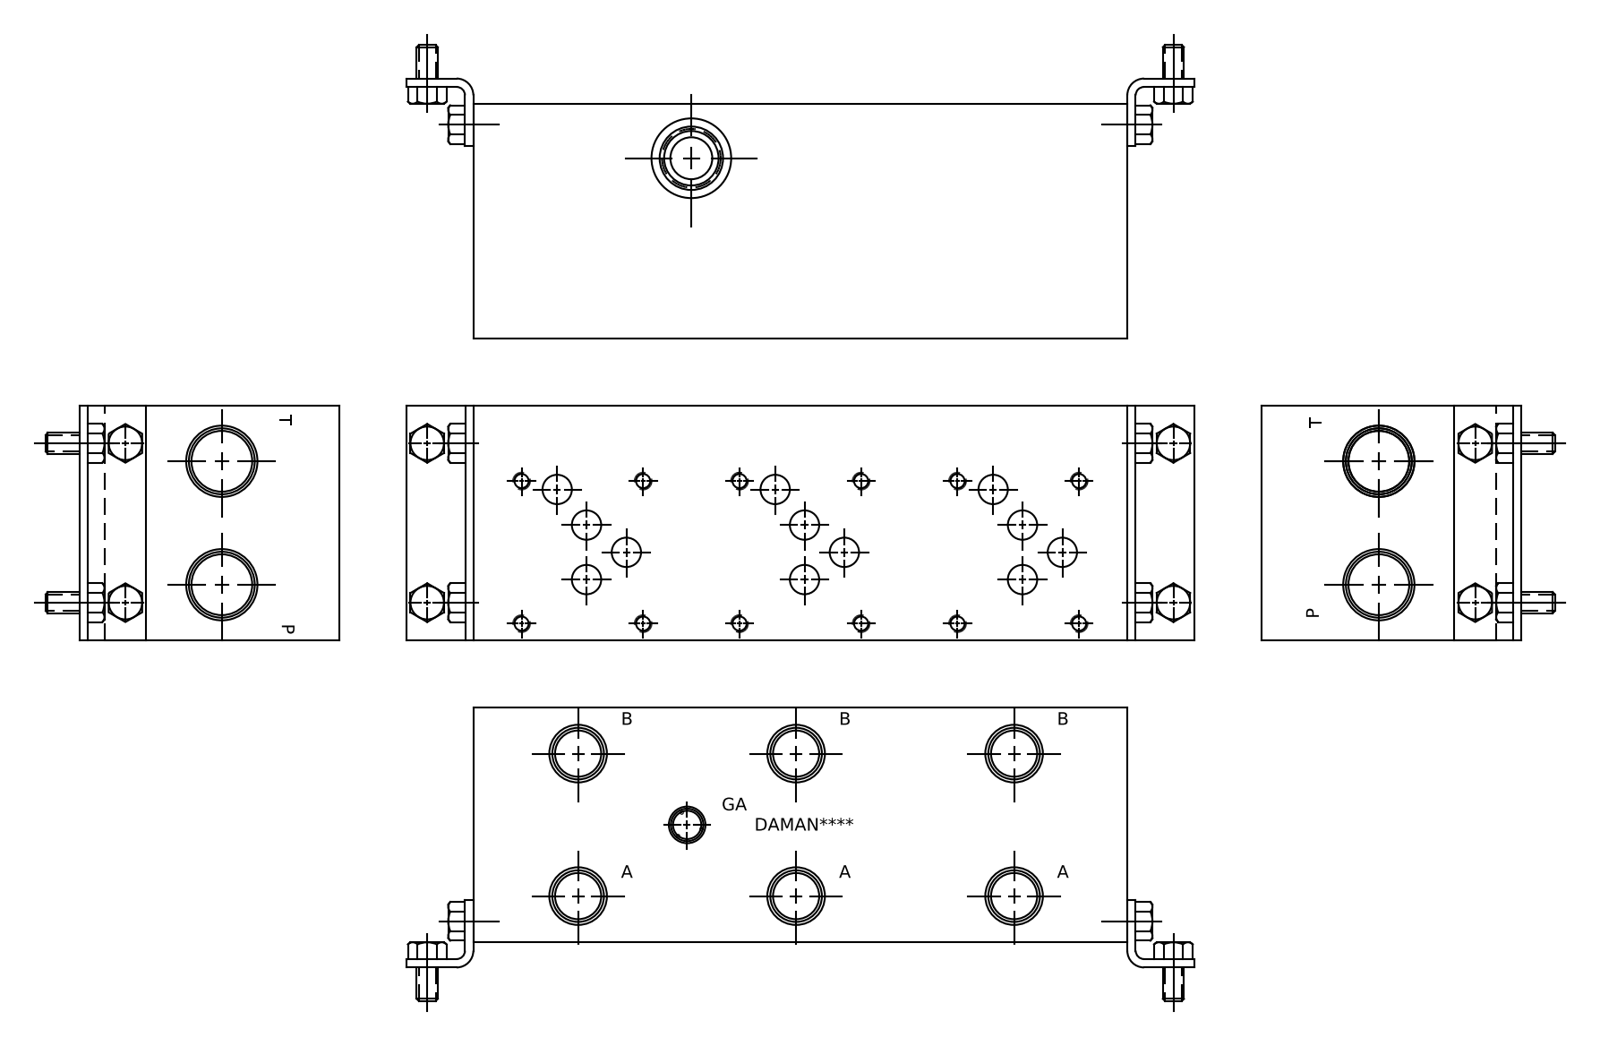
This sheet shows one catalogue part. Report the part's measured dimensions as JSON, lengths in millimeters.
{"part_name": "Part_AD05P033P~C_3D", "step_written_by": "Autodesk Inventor 2019 (AUTOMOTIVE_DESIGN)", "units": "millimeters", "bodies": {"solids": 1, "faces": 705, "planar": 394, "cylindrical": 72, "other": 239}, "overall_size": [247.65, 88.9, 88.9], "volume_mm3": 1849000, "surface_area_mm2": 128381, "round_holes": [[5.11, 12], [6.35, 12], [11.13, 11], [17.48, 6], [21.59, 6], [6.53, 2], [7.92, 2], [23.01, 2], [26.92, 2], [10.72, 1], [11.11, 1], [13.87, 1]], "face_to_face_distances": [88.9, 247.65, 15.37, 73.53, 15.85, 231.8, 215.95, 1, 88.11, 72.74], "hole_center_spacings": [82.55, 165.1, 98.63, 46.05, 70.95, 53.98, 36.5, 43]}
